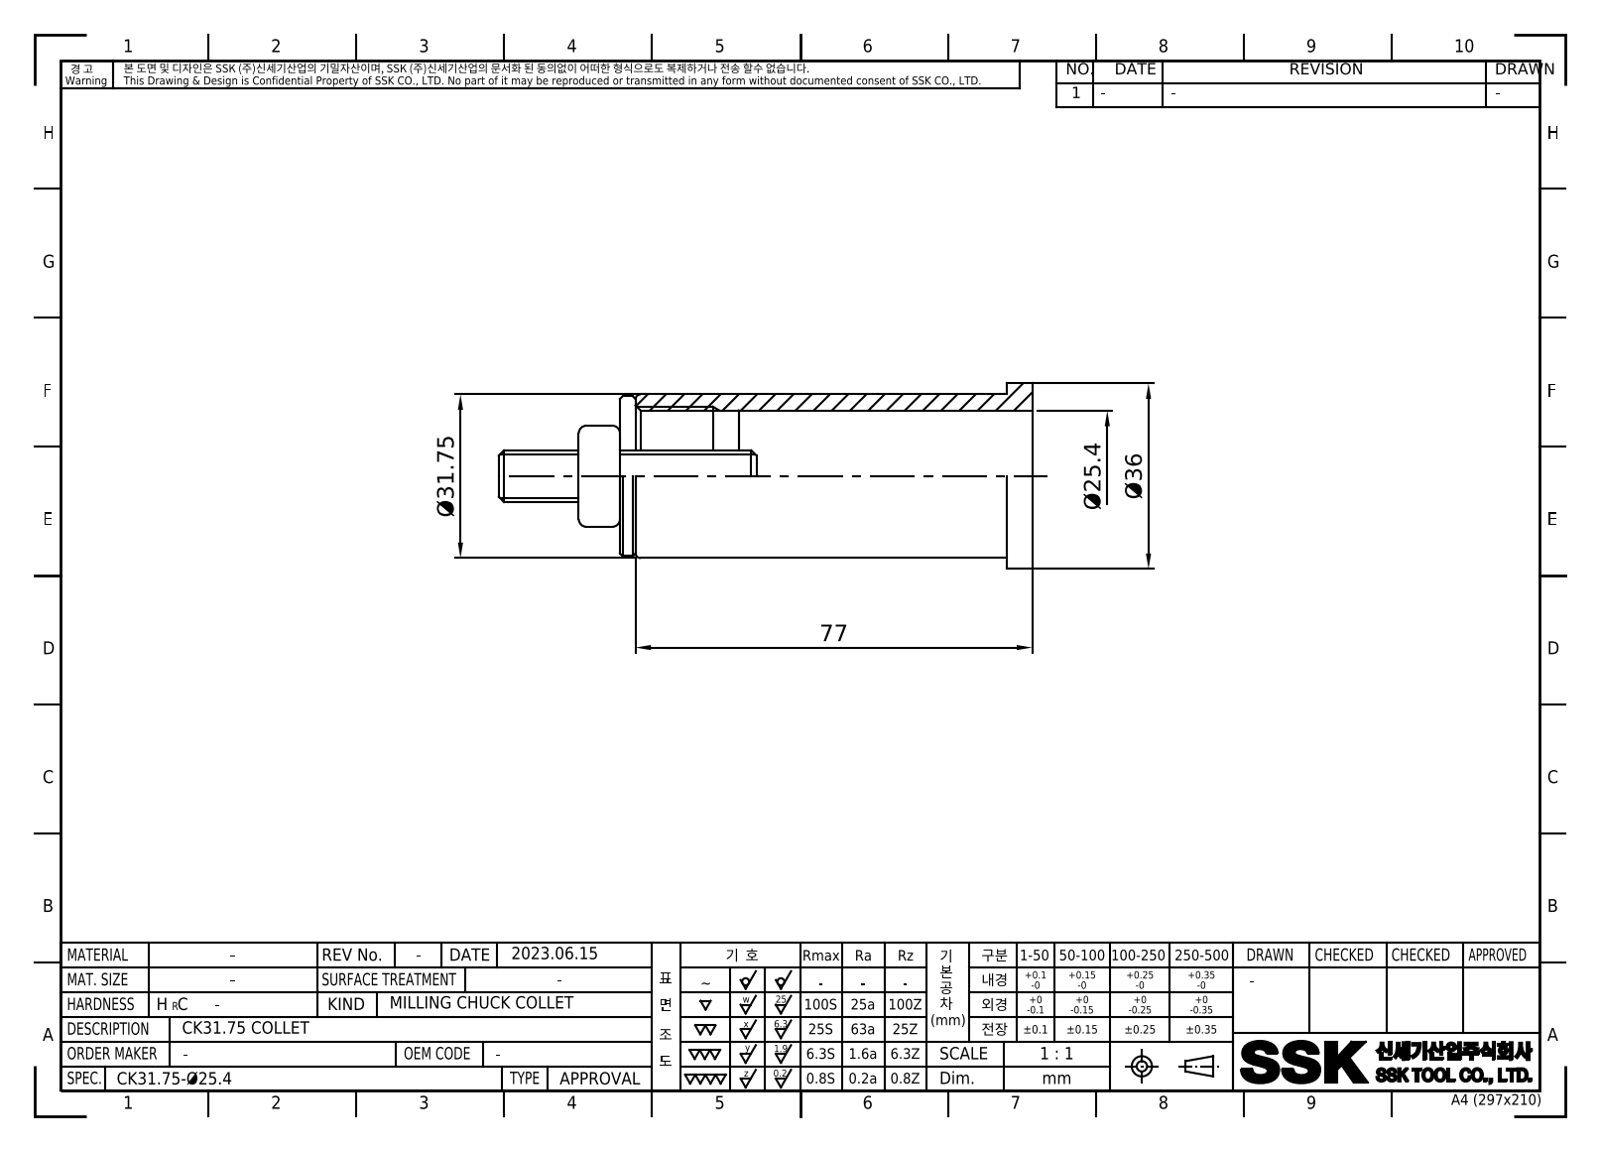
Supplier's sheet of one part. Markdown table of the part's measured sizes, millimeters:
| quantity | value |
| --- | --- |
| part name | LO-CK31.75-25.4 |
| STEP written by | Autodesk Inventor 2022 (AUTOMOTIVE_DESIGN) |
| units | millimeters |
| bodies | 1 solid, 8 faces (4 planar, 4 cylindrical, 0 other) |
| overall size | 77 × 36 × 36 |
| volume | 23 096 mm³ |
| surface area | 14 914 mm² |
| round holes (diameter × count) | 25.38 × 1, 25.4 × 1 |
| round bosses / shafts (diameter × count) | 36 × 1, 31.75 × 1 |
| main face-to-face distances | 77, 72, 5, 19, 53, 58 |
